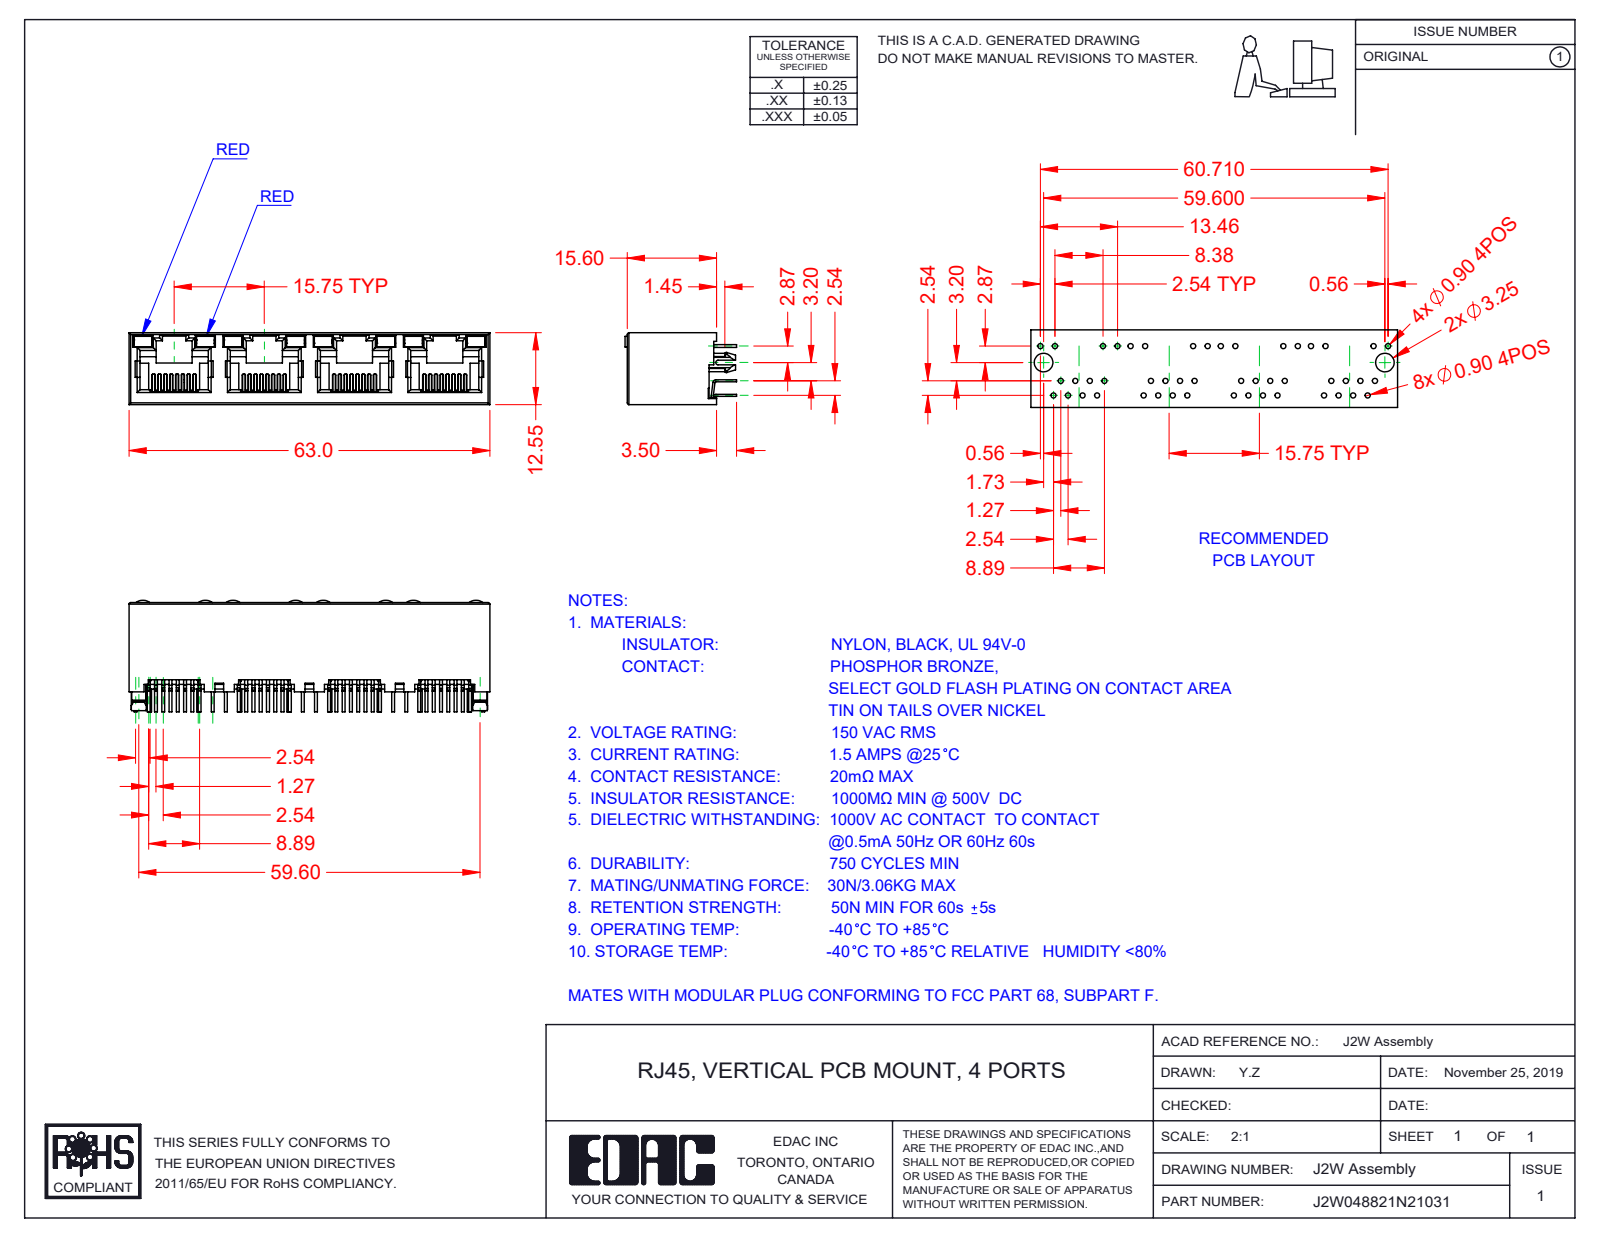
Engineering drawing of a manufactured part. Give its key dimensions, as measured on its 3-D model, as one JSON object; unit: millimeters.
{"part_name": "J2W048821N22131; 2W LED RH_2-Red; 2W LED LH_2-Red; 2W Contact Lock (+2 more)", "step_written_by": "SolidWorks 2016 (CONFIG_CONTROL_DESIGN)", "units": "millimeters", "bodies": {"solids": 45, "faces": 3135, "planar": 2600, "cylindrical": 477, "other": 58}, "overall_size": [63, 19.5, 12.55], "volume_mm3": 5335, "surface_area_mm2": 13144, "partial_cylinders_radius": [[0.15, 64], [0.2, 29], [0.5, 28], [0.3, 14], [0.45, 8], [2, 8], [0.25, 2], [1.5, 2]], "face_to_face_distances": [12.55, 11.9, 0.65, 15.75, 0.36, 1.5, 0.78, 0.6, 11.3, 31.5]}
